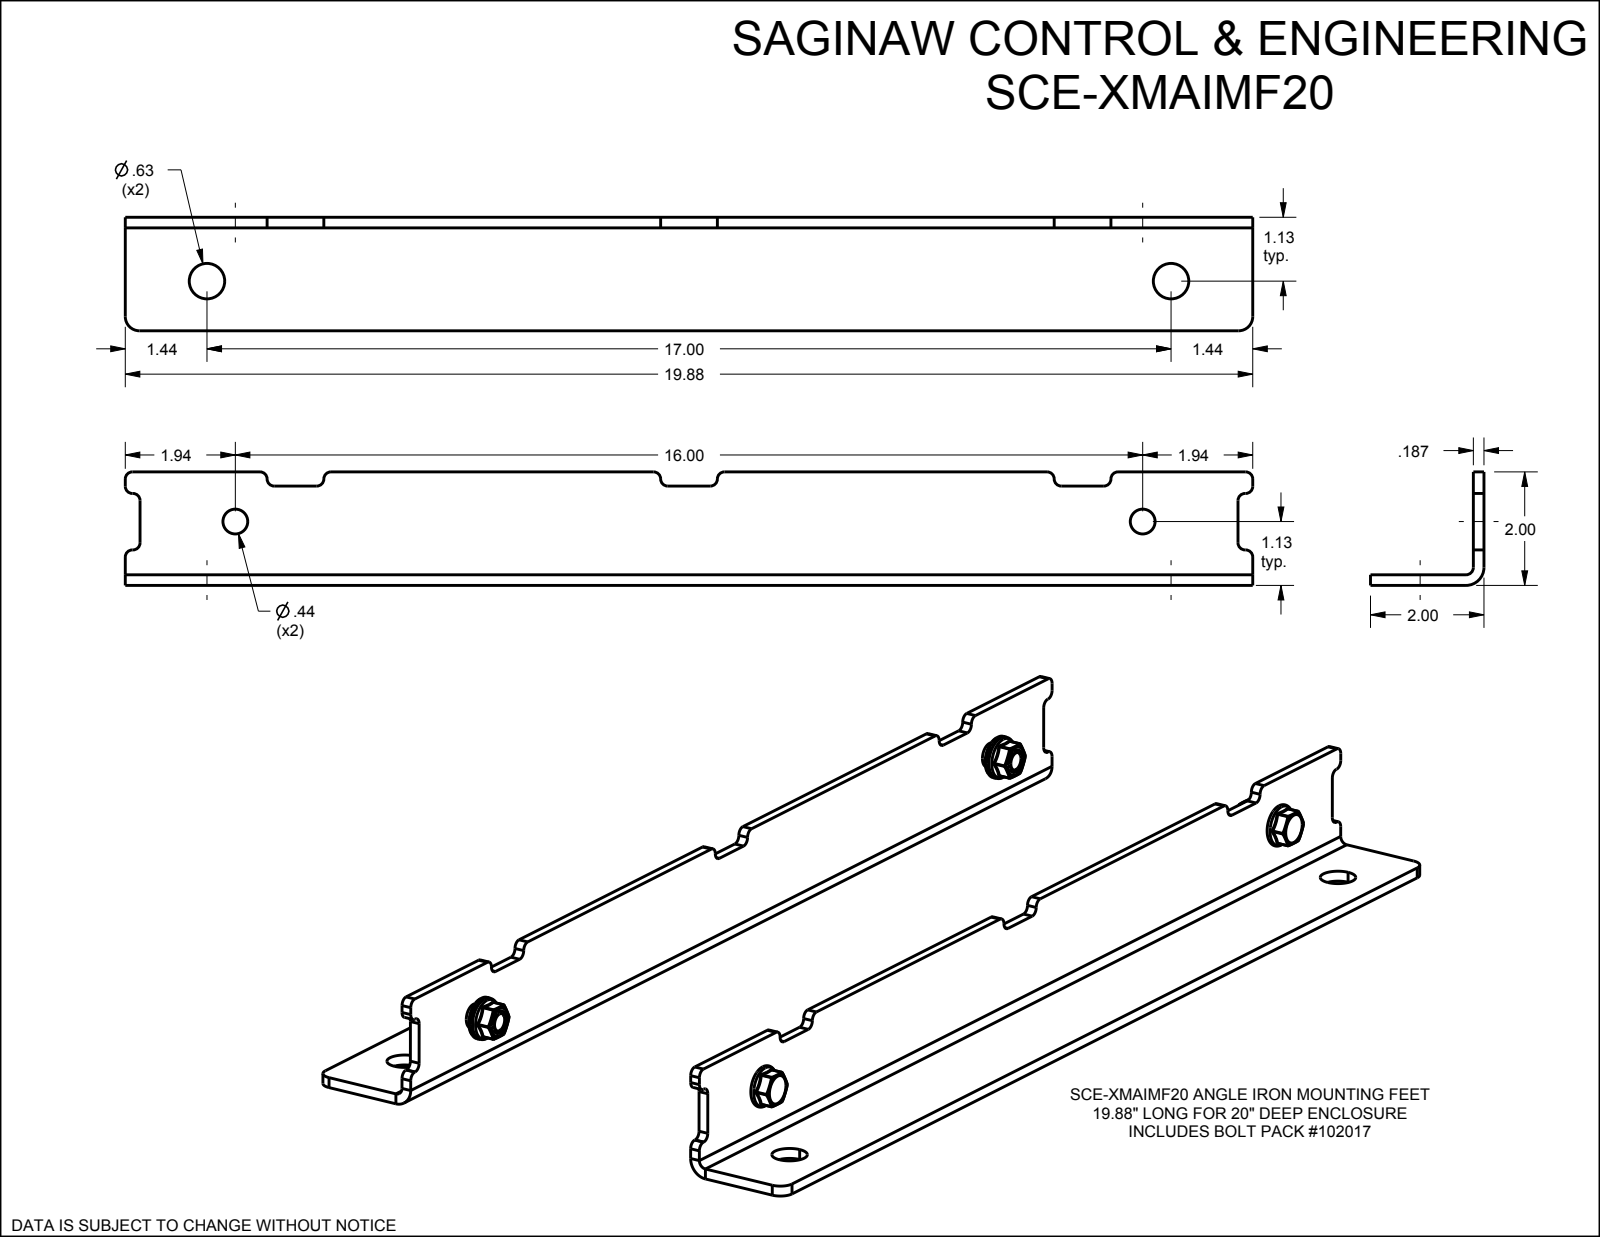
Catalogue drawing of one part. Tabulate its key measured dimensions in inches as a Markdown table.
| quantity | value |
| --- | --- |
| part name | SCE-XMAIMF20 |
| STEP written by | SolidWorks 2019 (CONFIG_CONTROL_DESIGN) |
| units | inches |
| bodies | 14 solids, 488 faces (128 planar, 132 cylindrical, 228 other) |
| overall size | 19.875 × 10 × 2 |
| volume | 27.89 in³ |
| surface area | 326.3 in² |
| round holes (diameter × count) | 0.367 × 2, 0.4 × 2, 0.43 × 2, 0.437 × 2, 0.625 × 2, 0.625 × 2 |
| round bosses / shafts (diameter × count) | 0.75 × 2, 0.7 × 2, 0.373 × 2 |
| partial cylindrical surfaces (radius × count) | 0.125 × 25, 0.01 × 18, 0.25 × 4, 0.13 × 2, 0.317 × 2 |
| main face-to-face distances | 0.187, 6.187, 6.374, 6, 1.813, 2, 8, 8.187, 10.001, 2.223 |
| hole center spacings | 8.25, 16.995, 18.892, 15.995, 16 |
